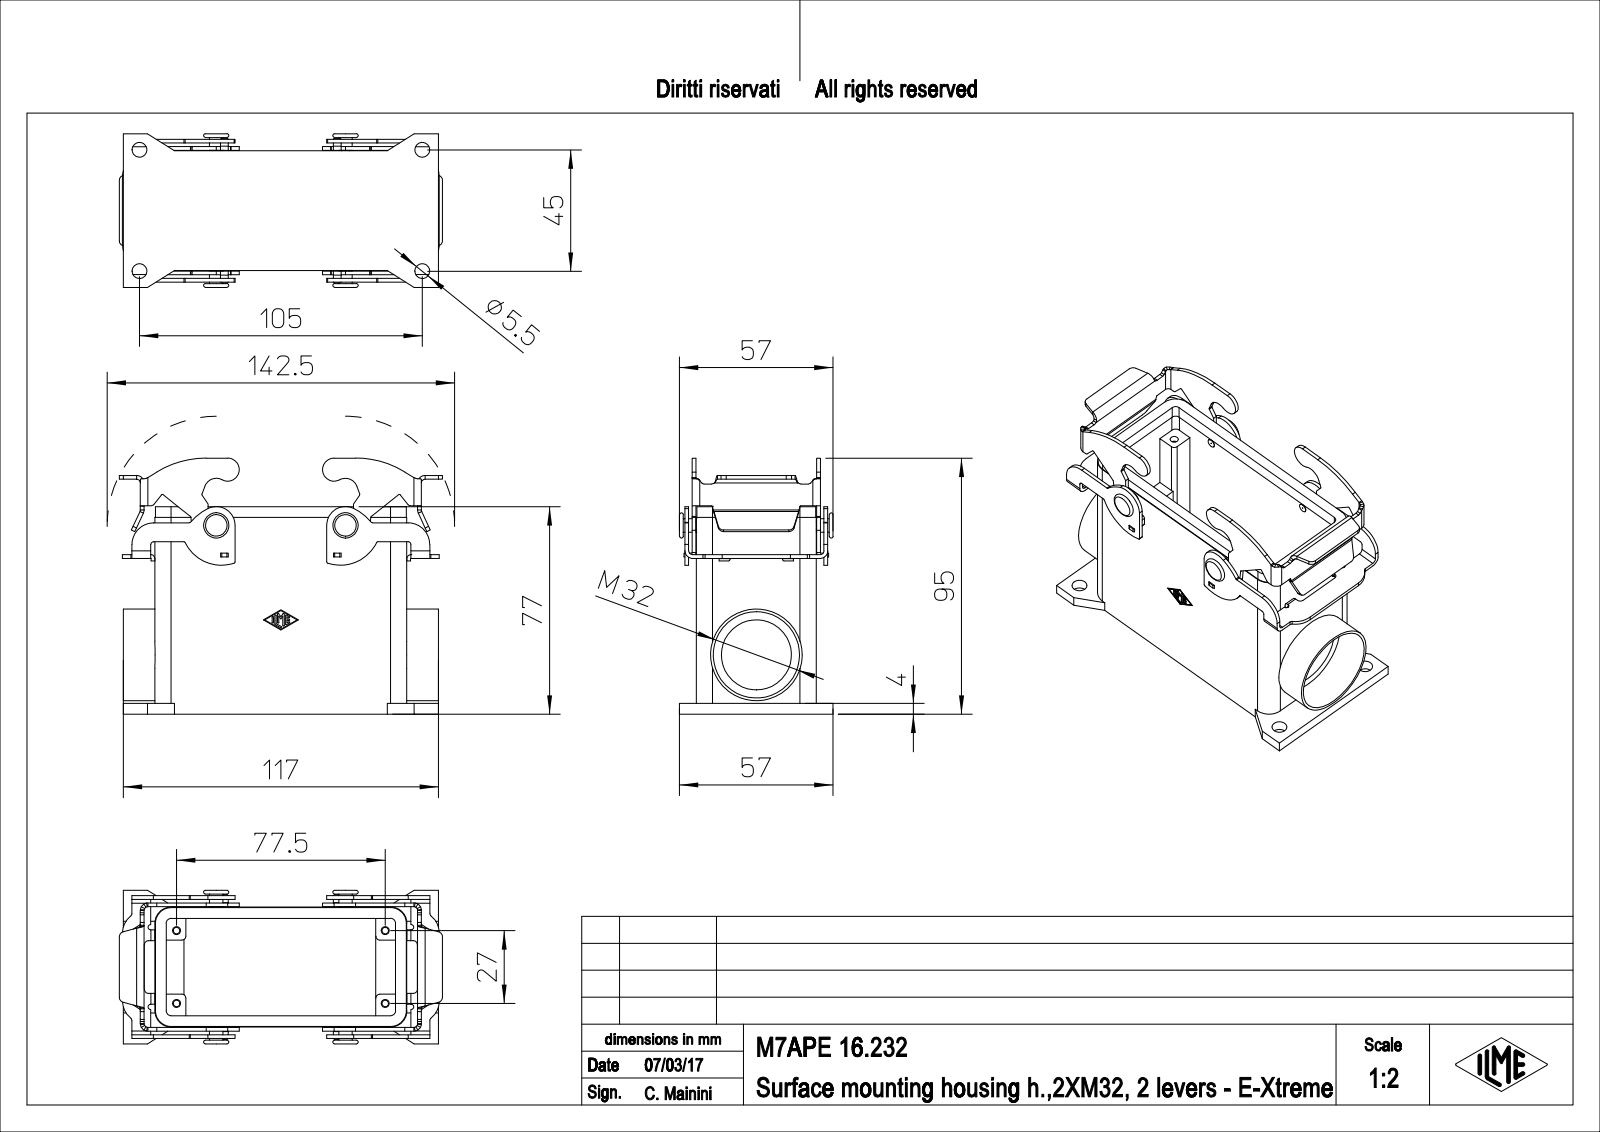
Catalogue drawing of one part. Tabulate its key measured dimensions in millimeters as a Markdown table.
| quantity | value |
| --- | --- |
| part name | M7APE_16.232 |
| STEP written by | PTC Creo Elements/Direct Modeling 19.0E 27-Jun-2016 (C) Parametric Technology GmbH (AUTOMOTIVE_DESIGN) |
| units | millimeters |
| bodies | 1 solid, 613 faces (295 planar, 272 cylindrical, 46 other) |
| overall size | 119.97 × 95 × 57 |
| volume | 121 318 mm³ |
| surface area | 70 801 mm² |
| round holes (diameter × count) | 2.46 × 4, 3 × 4, 5.5 × 4, 3.5 × 2, 26 × 1, 32 × 1 |
| round bosses / shafts (diameter × count) | 5 × 2, 3.2 × 2, 3 × 2, 34 × 1 |
| partial cylindrical surfaces (radius × count) | 0.5 × 22, 1 × 18, 0.25 × 16, 1.5 × 14, 2 × 12, 1.4 × 10, 2.8 × 10, 8 × 6 |
| main face-to-face distances | 4, 40.5, 1.4, 44.5, 36.5, 2.7, 48.9, 8.25, 1.55, 5.55 |
| hole center spacings | 16.43, 38.54, 91.69, 98.09, 27, 45, 77.5, 82.07 |
